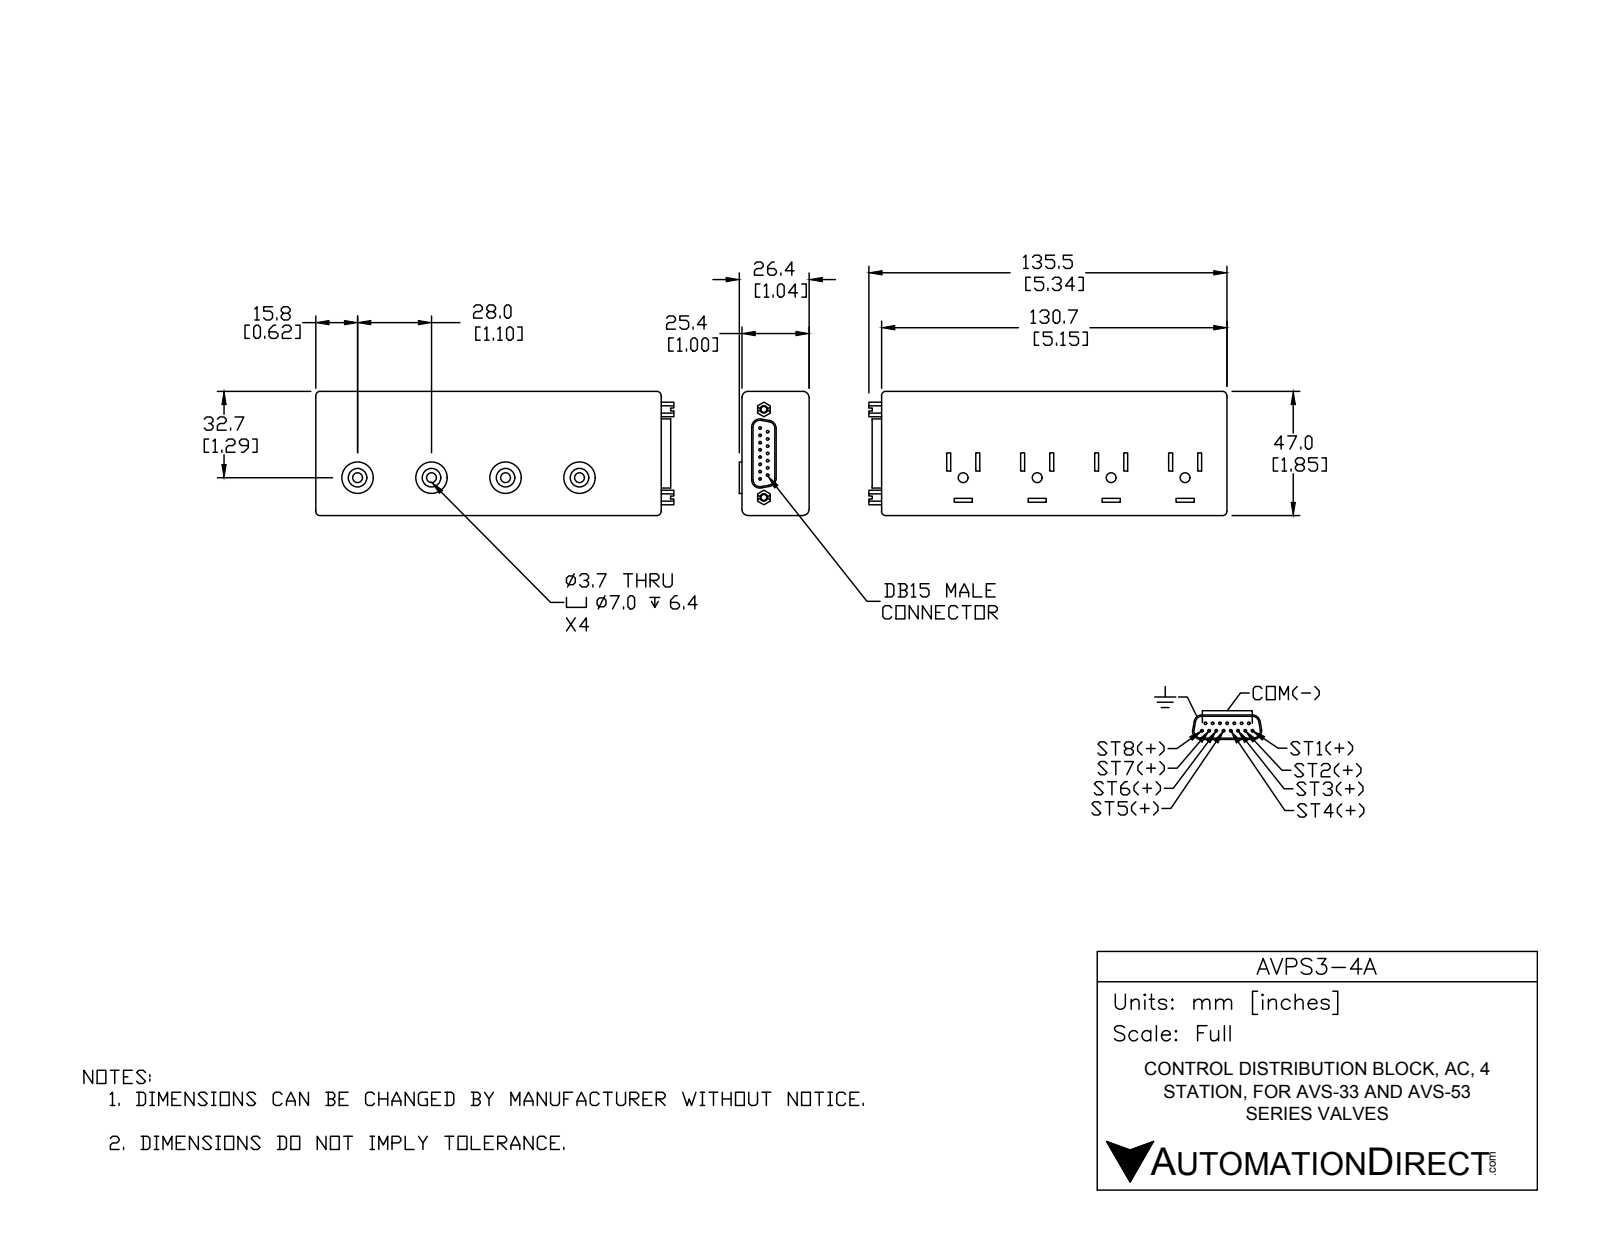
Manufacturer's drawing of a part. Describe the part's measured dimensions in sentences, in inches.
The part is named "AVPS3-4A". Its 3-D file was written by "SolidWorks 2016 (AUTOMOTIVE_DESIGN)". It is 1 solid with 219 faces: 127 planar, 80 cylindrical and 12 other. Overall it measures 5.335 by 1.85 by 1.04 inches. Its volume is 9.326 cubic inches and its surface area 38.06 square inches. Round holes: 4 of diameter 0.145, 4 of diameter 0.275, 2 of diameter 0.089. Round bosses or shafts: 15 of diameter 0.039, 4 of diameter 0.469. Partial cylindrical surfaces (rounded edges, fillets, slot ends): 8 of radius 0.062, 4 of radius 0.09, 4 of radius 0.102, 4 of radius 0.122. The main face-to-face distances are 1, 1.85, 5.146, 1.102, 0.059, 2.204, 0.433, 0.04, 1.04, 1.161. The hole center spacings are 1.102, 2.204, 1.311, 3.306.
